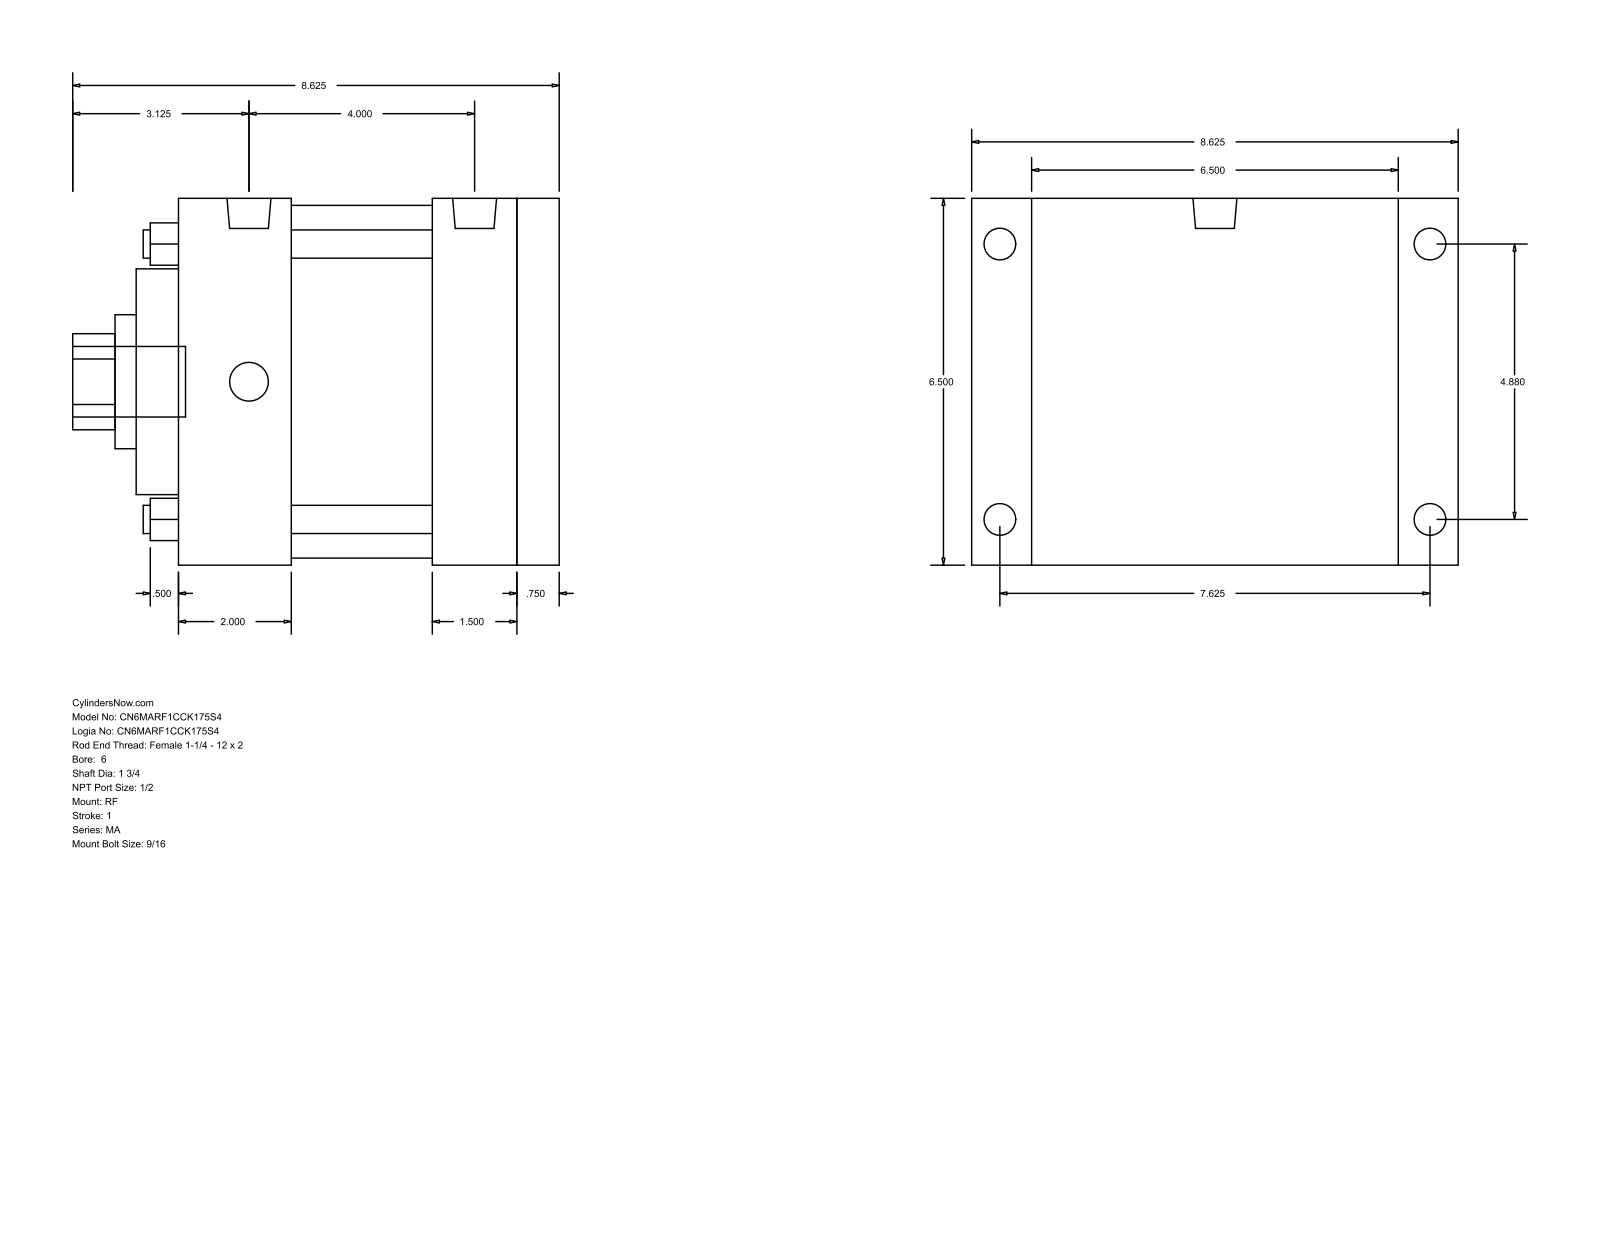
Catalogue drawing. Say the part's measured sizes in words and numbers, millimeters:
The part is named "MA_RF__0600_1.75". Its 3-D file was written by "GSSL Pune (CONFIG_CONTROL_DESIGN)". It is 0 solids with 94 faces: 65 planar, 29 cylindrical and 0 other. Overall it measures 219.07 by 219.07 by 165.1 millimeters. Round holes: 4 of diameter 12.7, 1 of diameter 44.45, 1 of diameter 60.33, 1 of diameter 101.6, 1 of diameter 158.75. Round bosses or shafts: 4 of diameter 17.46, 4 of diameter 14.29, 2 of diameter 19.77, 1 of diameter 31.75. Partial cylindrical surfaces (rounded edges, fillets, slot ends): 1 of radius 21.63. The main face-to-face distances are 165.1, 171.45, 19.04, 152.41, 19.05, 38.1, 50.8, 101.61, 120.65, 114.31. The hole center spacings are 87.65, 123.96, 175.31.
